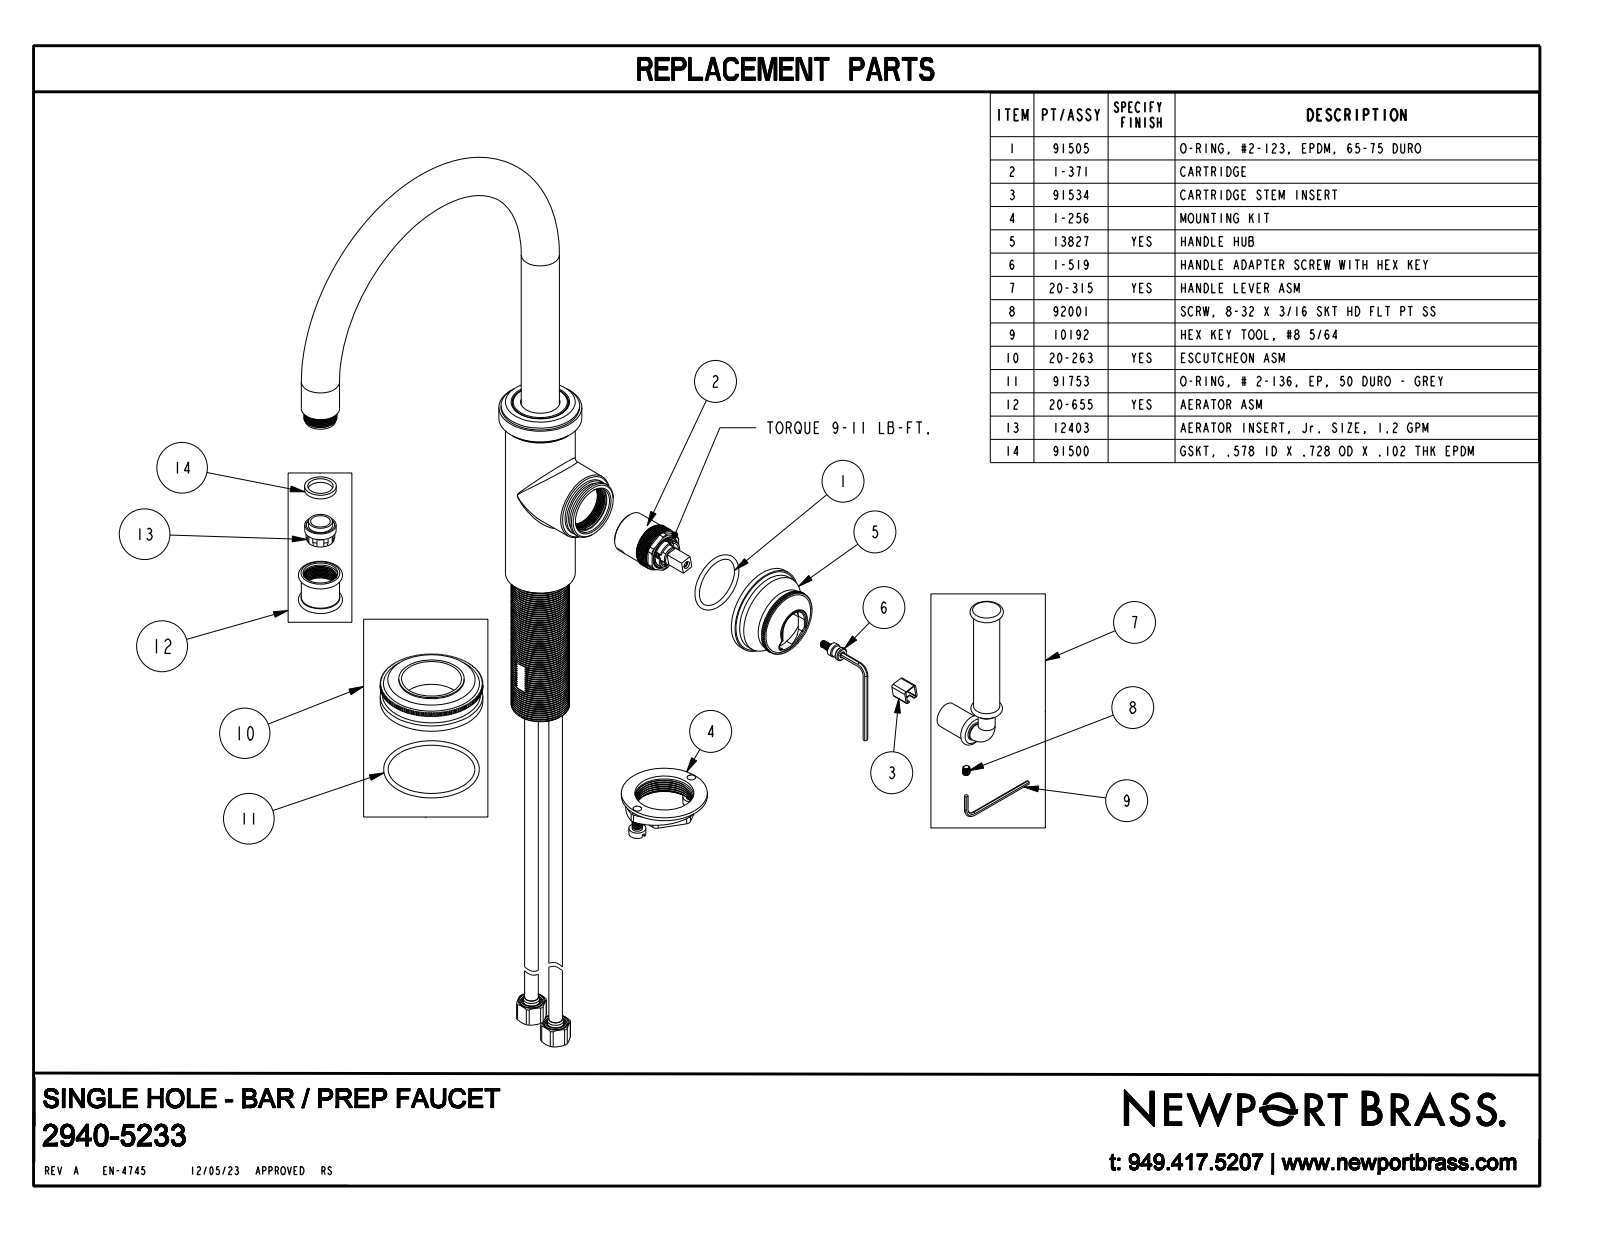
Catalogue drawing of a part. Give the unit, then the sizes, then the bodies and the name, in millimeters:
Units: millimetres
Overall size (bounding box): 343.8 × 223.7 × 125.8
Round holes (diameter × count): ⌀10.4 ×1, ⌀14.2 ×1, ⌀15.7 ×1, ⌀17.6 ×1, ⌀22.9 ×1, ⌀34.5 ×1
Round bosses / shafts (diameter × count): ⌀22.2 ×2, ⌀9.9 ×2, ⌀59.7 ×1, ⌀57.2 ×1, ⌀51.6 ×1, ⌀48.3 ×1, ⌀47 ×1, ⌀45.7 ×1
Partial cylindrical surfaces — rounded edges, fillets, slot ends (radius × count): R9 ×3, R0.5 ×2, R8.6 ×1, R11.4 ×1, R19.7 ×1
Main face-to-face distances: 15.5, 2.5, 20.3, 110.5, 113, 137.4, 121.9, 137.4, 121.9, 13
Hole centre spacings: 86.3, 181, 200.5
Volume: 443 400 mm³ · Surface area: 71 290 mm²
Bodies: 1 solid, 823 faces (470 planar, 287 cylindrical, 66 other)
Part name (STEP PRODUCT): 2940-5233_SW0001
STEP written by: CREO PARAMETRIC BY PTC INC, 2023134 (CONFIG_CONTROL_DESIGN)
